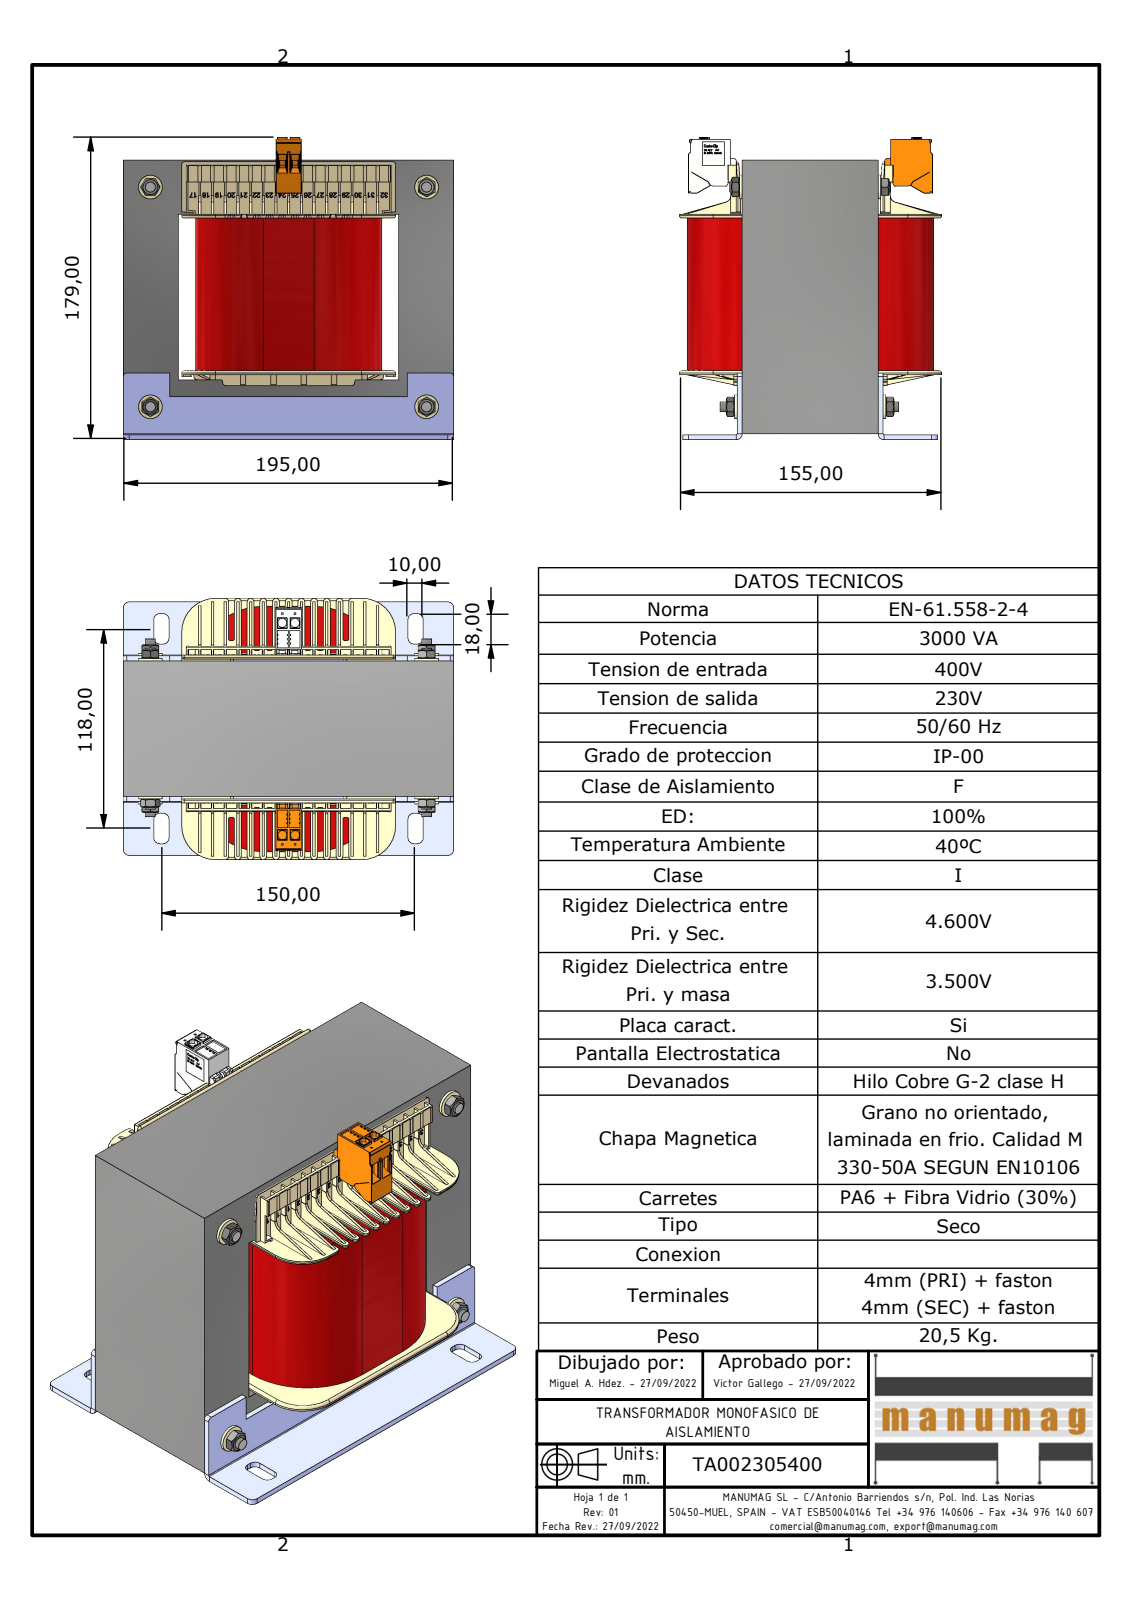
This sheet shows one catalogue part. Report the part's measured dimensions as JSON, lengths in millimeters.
{"part_name": "TA002305400; EI195 x 162 - 80 (Rc65); EI192_82_AK_25372_1_Wz837 BOBINADO; EI192_82_AK_25372_1_Wz837 (+8 more)", "step_written_by": "Autodesk Inventor 2023 (AUTOMOTIVE_DESIGN)", "units": "millimeters", "bodies": {"solids": 27, "faces": 5958, "planar": 3976, "cylindrical": 692, "other": 1290}, "overall_size": [195, 179, 154.6], "volume_mm3": 2988000, "surface_area_mm2": 469370, "round_holes": [[4.92, 4], [6, 4], [11, 4], [9.9, 2]], "round_bosses_or_shafts": [[14, 4], [7.6, 4]], "partial_cylinders_radius": [[0.15, 164], [0.2, 70], [1, 52], [1.5, 44], [0.5, 28], [1.95, 22], [3.5, 22], [0.3, 12]], "face_to_face_distances": [130, 32.5, 80, 162.5, 3, 2.4, 92.6, 65, 32, 97.5], "hole_center_spacings": [130, 163, 208.49]}
